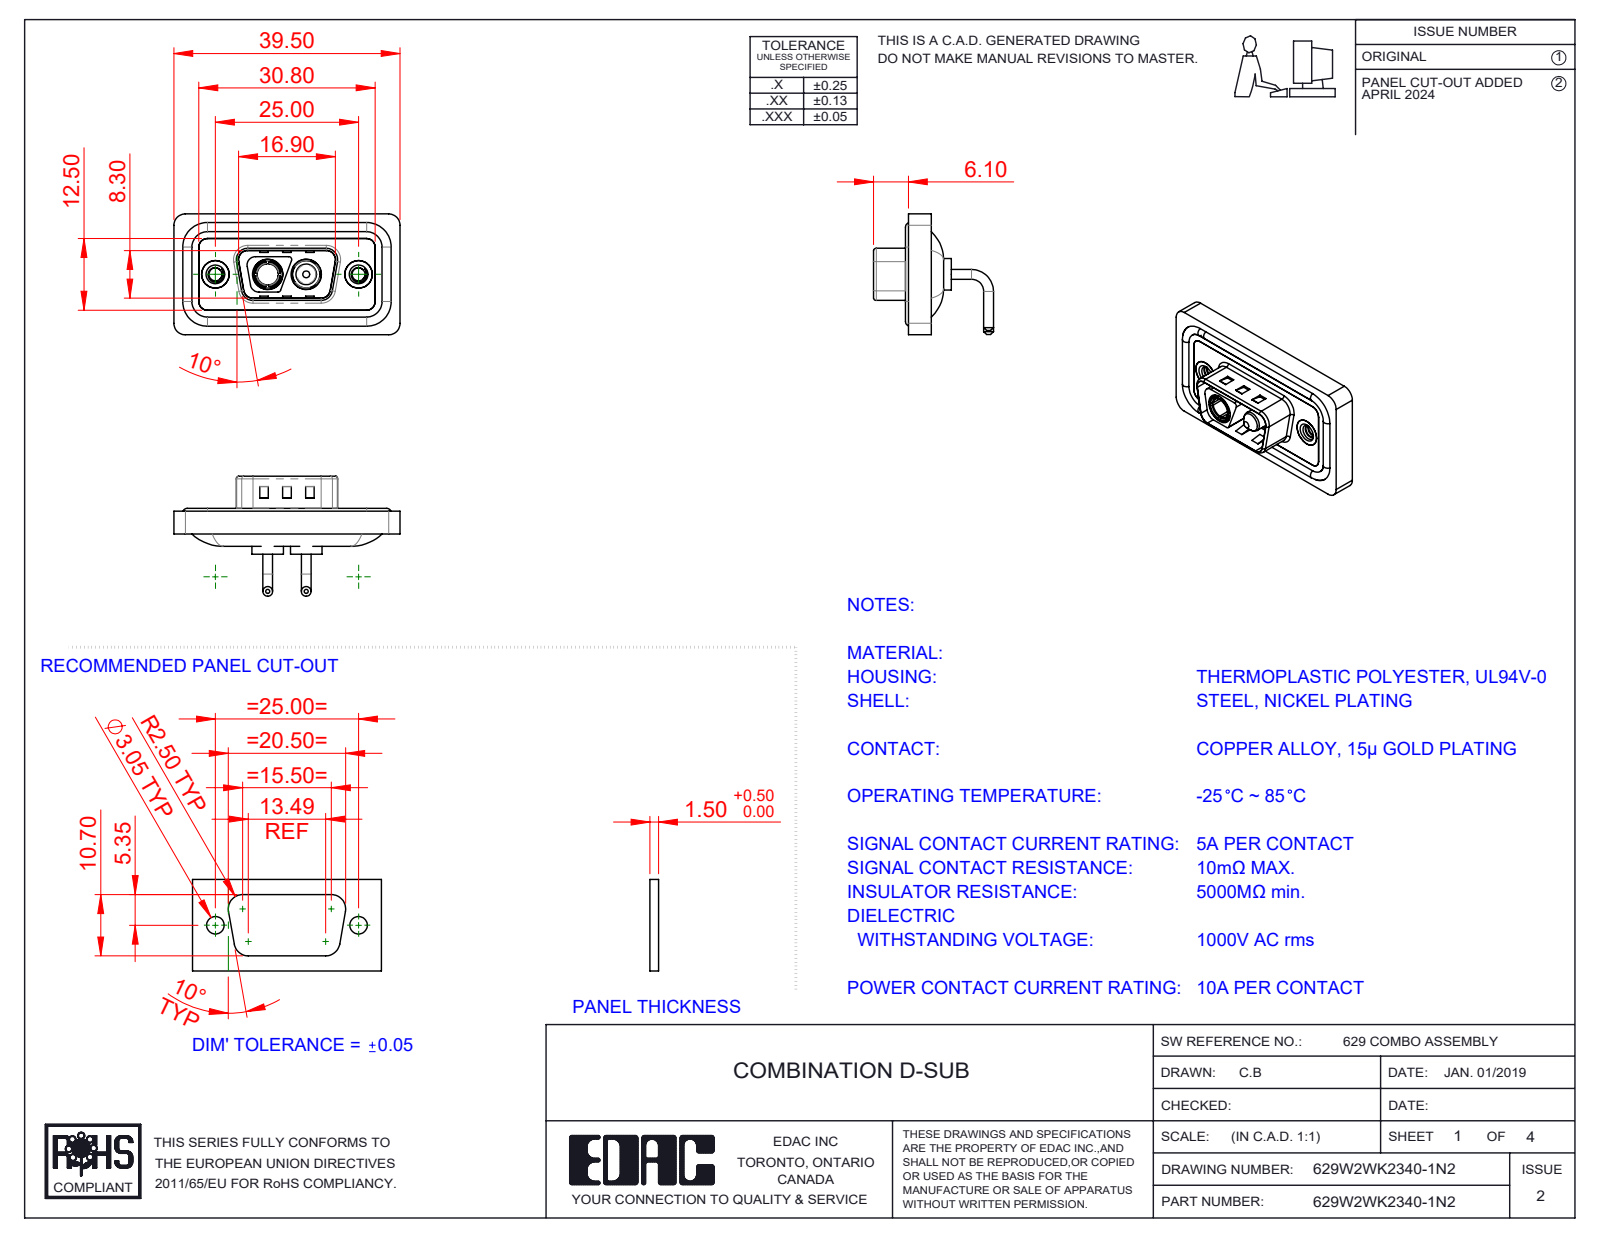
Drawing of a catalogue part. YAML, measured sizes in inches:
part_name: "629Combo Waterproof Housing_09 Contacts; Power Socket_10A RA; 629Combo Shell Rear_09 Contacts; 629W2WK2340-1N2 (+4 more)"
step_written_by: "SolidWorks 2023 (CONFIG_CONTROL_DESIGN)"
units: inches
bodies: {solids: 11, faces: 542, planar: 189, cylindrical: 231, other: 122}
overall_size: [1.555, 0.831, 0.825]
volume: 0.279
surface_area: 11.51
round_holes:
  - {diameter: 0.089, count: 2}
  - {diameter: 0.157, count: 2}
  - {diameter: 0.189, count: 2}
  - {diameter: 0.191, count: 2}
  - {diameter: 0.197, count: 2}
  - {diameter: 0.209, count: 2}
  - {diameter: 0.146, count: 1}
round_bosses_or_shafts:
  - {diameter: 0.067, count: 4}
  - {diameter: 0.063, count: 4}
  - {diameter: 0.217, count: 2}
  - {diameter: 0.205, count: 2}
  - {diameter: 0.193, count: 2}
  - {diameter: 0.187, count: 2}
  - {diameter: 0.148, count: 2}
  - {diameter: 0.195, count: 1}
partial_cylinders:
  - {radius: 0.059, count: 20}
  - {radius: 0.079, count: 18}
  - {radius: 0.02, count: 10}
  - {radius: 0.063, count: 8}
  - {radius: 0.01, count: 4}
  - {radius: 0.024, count: 4}
  - {radius: 0.026, count: 4}
  - {radius: 0.035, count: 4}
face_to_face_distances: [0.016, 0.114, 0.043, 0.031, 0.083, 0.098, 0.122, 0.063, 0.177, 0.059]
hole_center_spacings: [0.36, 0.624, 0.265, 0.984]
